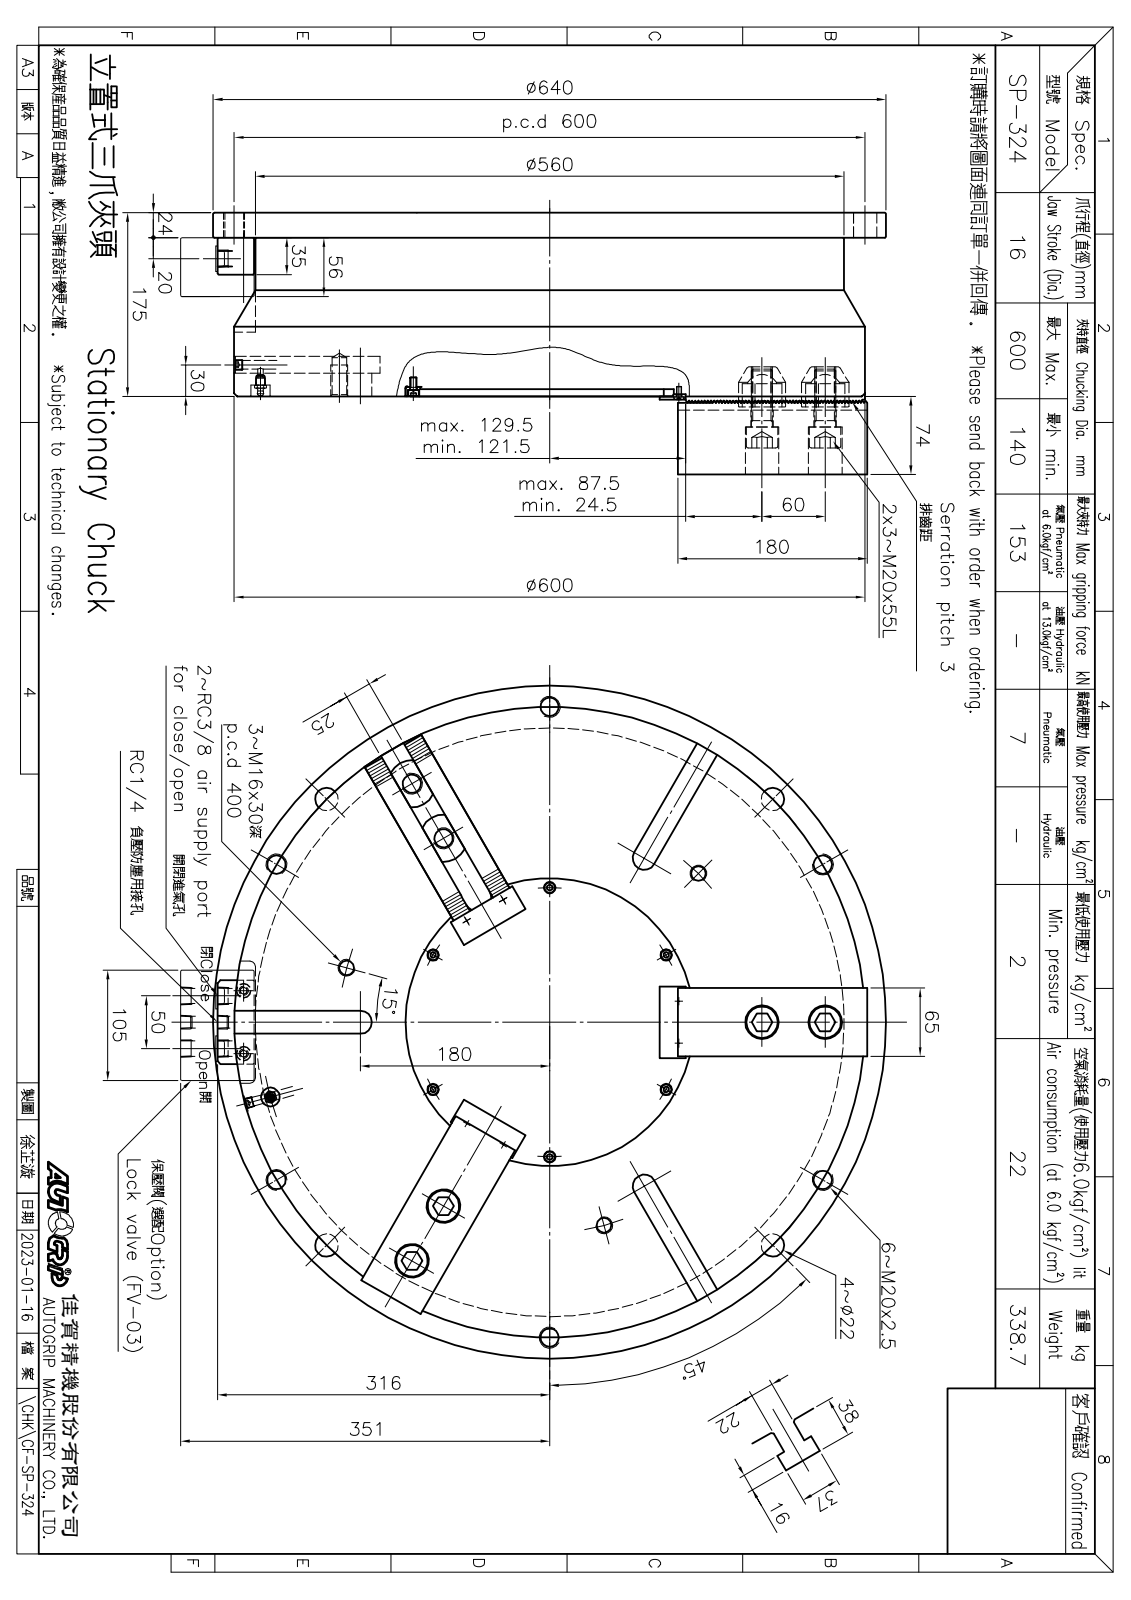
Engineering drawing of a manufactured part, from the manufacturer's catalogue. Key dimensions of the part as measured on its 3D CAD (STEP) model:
Part name (STEP PRODUCT): CF-SP-324-01000; 半圓頭六角孔螺栓_M4x8; CF-SP-316-09000; CF-SP-324-06000 (+8 more)
STEP written by: SolidWorks 2020 (CONFIG_CONTROL_DESIGN)
Units: millimetres
Bodies: 42 solids, 4604 faces (3390 planar, 950 cylindrical, 264 other)
Overall size (bounding box): 640 × 640 × 249.2
Volume: 49 660 000 mm³ · Surface area: 2 522 000 mm²
Round holes (diameter × count): ⌀10.2 ×12, ⌀17.5 ×12, ⌀5 ×7, ⌀5.5 ×7, ⌀32 ×7, ⌀6.6 ×6, ⌀10 ×6, ⌀11 ×6, ⌀21 ×6, ⌀14 ×5, ⌀22 ×4, ⌀6.8 ×2
Round bosses / shafts (diameter × count): ⌀30 ×6, ⌀20 ×6, ⌀10.5 ×6, ⌀6 ×6, ⌀9.5 ×3, ⌀7.6 ×3, ⌀5 ×3, ⌀4 ×3
Partial cylindrical surfaces — rounded edges, fillets, slot ends (radius × count): R0.1 ×321, R22.5 ×6, R11 ×3, R12.5 ×3, R18.5 ×3, R280 ×3, R10 ×2, R137 ×1
Main face-to-face distances: 24, 175, 151, 65, 14, 51, 110, 1.5, 86, 124
Hole centre spacings: 260, 128, 140.33, 502.28, 134.59, 192.14, 258.37, 318.14
